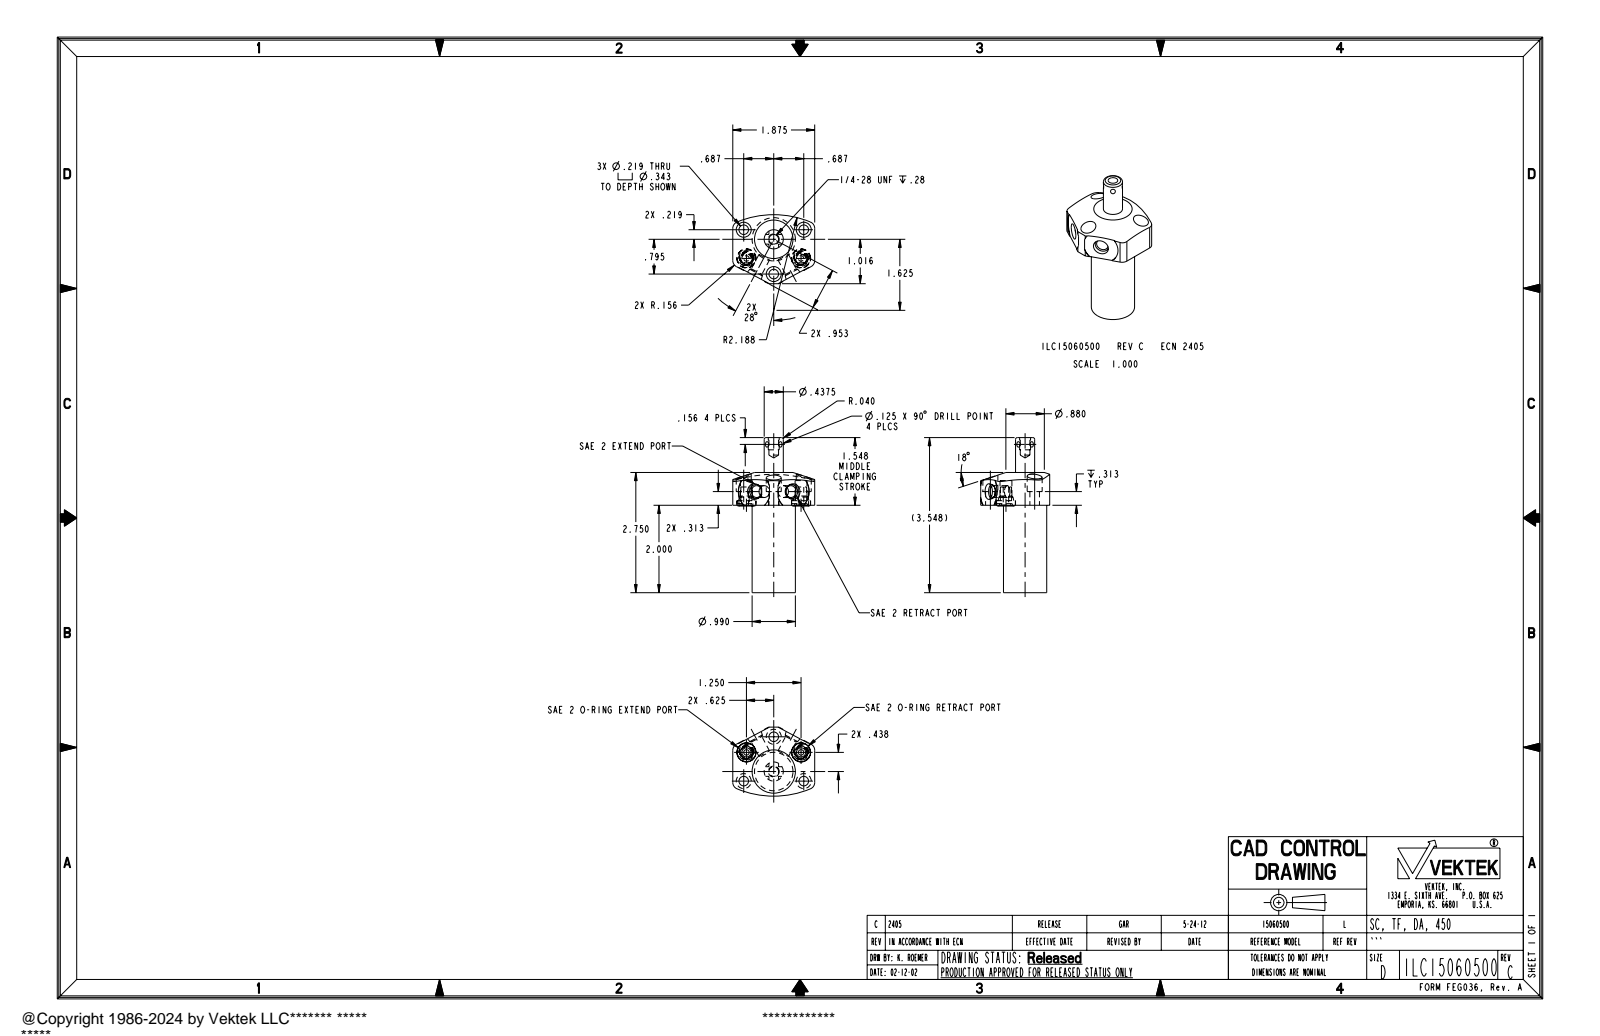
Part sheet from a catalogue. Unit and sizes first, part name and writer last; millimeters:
Units: millimetres
Overall size (bounding box): 90.1 × 47.6 × 40.1
Round holes (diameter × count): ⌀6.9 ×4, ⌀5.6 ×3, ⌀8.7 ×3, ⌀3.2 ×2, ⌀11.1 ×2, ⌀5.6 ×1
Round bosses / shafts (diameter × count): ⌀10.9 ×2, ⌀6.5 ×2, ⌀5.3 ×2, ⌀25.1 ×1, ⌀11.1 ×1, ⌀6.4 ×1
Partial cylindrical surfaces — rounded edges, fillets, slot ends (radius × count): R4 ×4, R10.5 ×2, R55.6 ×1
Main face-to-face distances: 50.8, 69.9, 19.1, 47.6, 8, 2.7, 58.8, 11.1, 65.2, 14.4
Hole centre spacings: 16.8, 18.3, 18.3, 19.4, 31.1, 37.3, 20.2, 31.8
Volume: 50 520 mm³ · Surface area: 13 740 mm²
Bodies: 1 solid, 132 faces (35 planar, 59 cylindrical, 38 other)
Part name (STEP PRODUCT): ILC15060500
STEP written by: PRO/ENGINEER BY PARAMETRIC TECHNOLOGY CORPORATION, 2007460 (AUTOMOTIVE_DESIGN_CC2)
